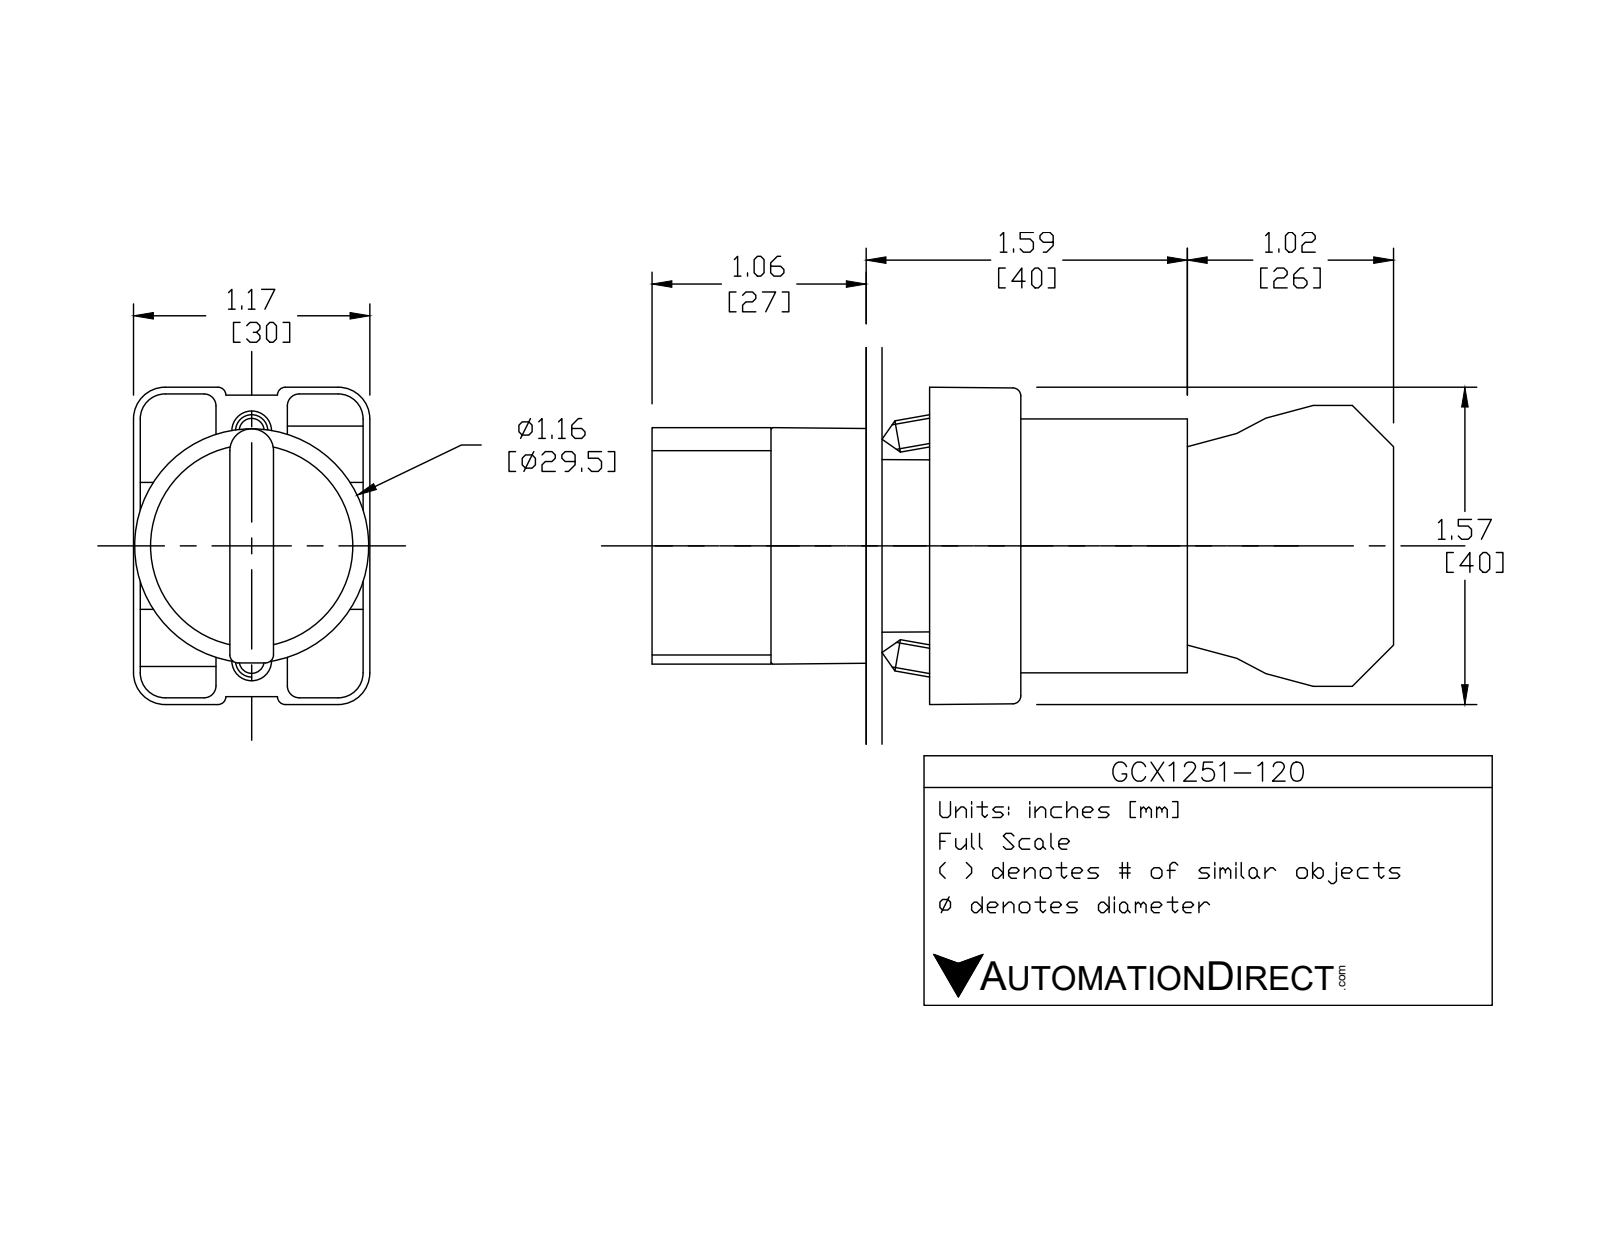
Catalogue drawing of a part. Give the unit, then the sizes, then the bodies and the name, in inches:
Units: inches
Overall size (bounding box): 3.653 × 1.581 × 1.177
Round holes (diameter × count): ⌀0.079 ×2, ⌀0.124 ×2, ⌀0.13 ×2, ⌀0.087 ×1, ⌀0.197 ×1, ⌀0.469 ×1, ⌀0.878 ×1, ⌀0.888 ×1, ⌀1.024 ×1
Round bosses / shafts (diameter × count): ⌀0.157 ×4, ⌀1.175 ×1, ⌀1.004 ×1, ⌀0.945 ×1, ⌀0.856 ×1, ⌀0.78 ×1, ⌀0.504 ×1
Partial cylindrical surfaces — rounded edges, fillets, slot ends (radius × count): R0.059 ×24, R0.041 ×12, R0.124 ×12, R0.157 ×12, R0.039 ×9, R0.128 ×2, R0.02 ×1, R0.063 ×1
Main face-to-face distances: 0.827, 2.02, 1.193, 0.579, 1.244, 1.171, 0.472, 0.469, 0.031, 0.033
Hole centre spacings: 0.236, 0.544, 0.472, 0.49
Volume: 2.799 in³ · Surface area: 39 in²
Bodies: 8 solids, 445 faces (263 planar, 151 cylindrical, 31 other)
Part name (STEP PRODUCT): GCX1251-120; ECX1050; GCX1251 OPERATOR; ecx1029 (+1 more)
STEP written by: SolidWorks 2016 (AUTOMOTIVE_DESIGN)
